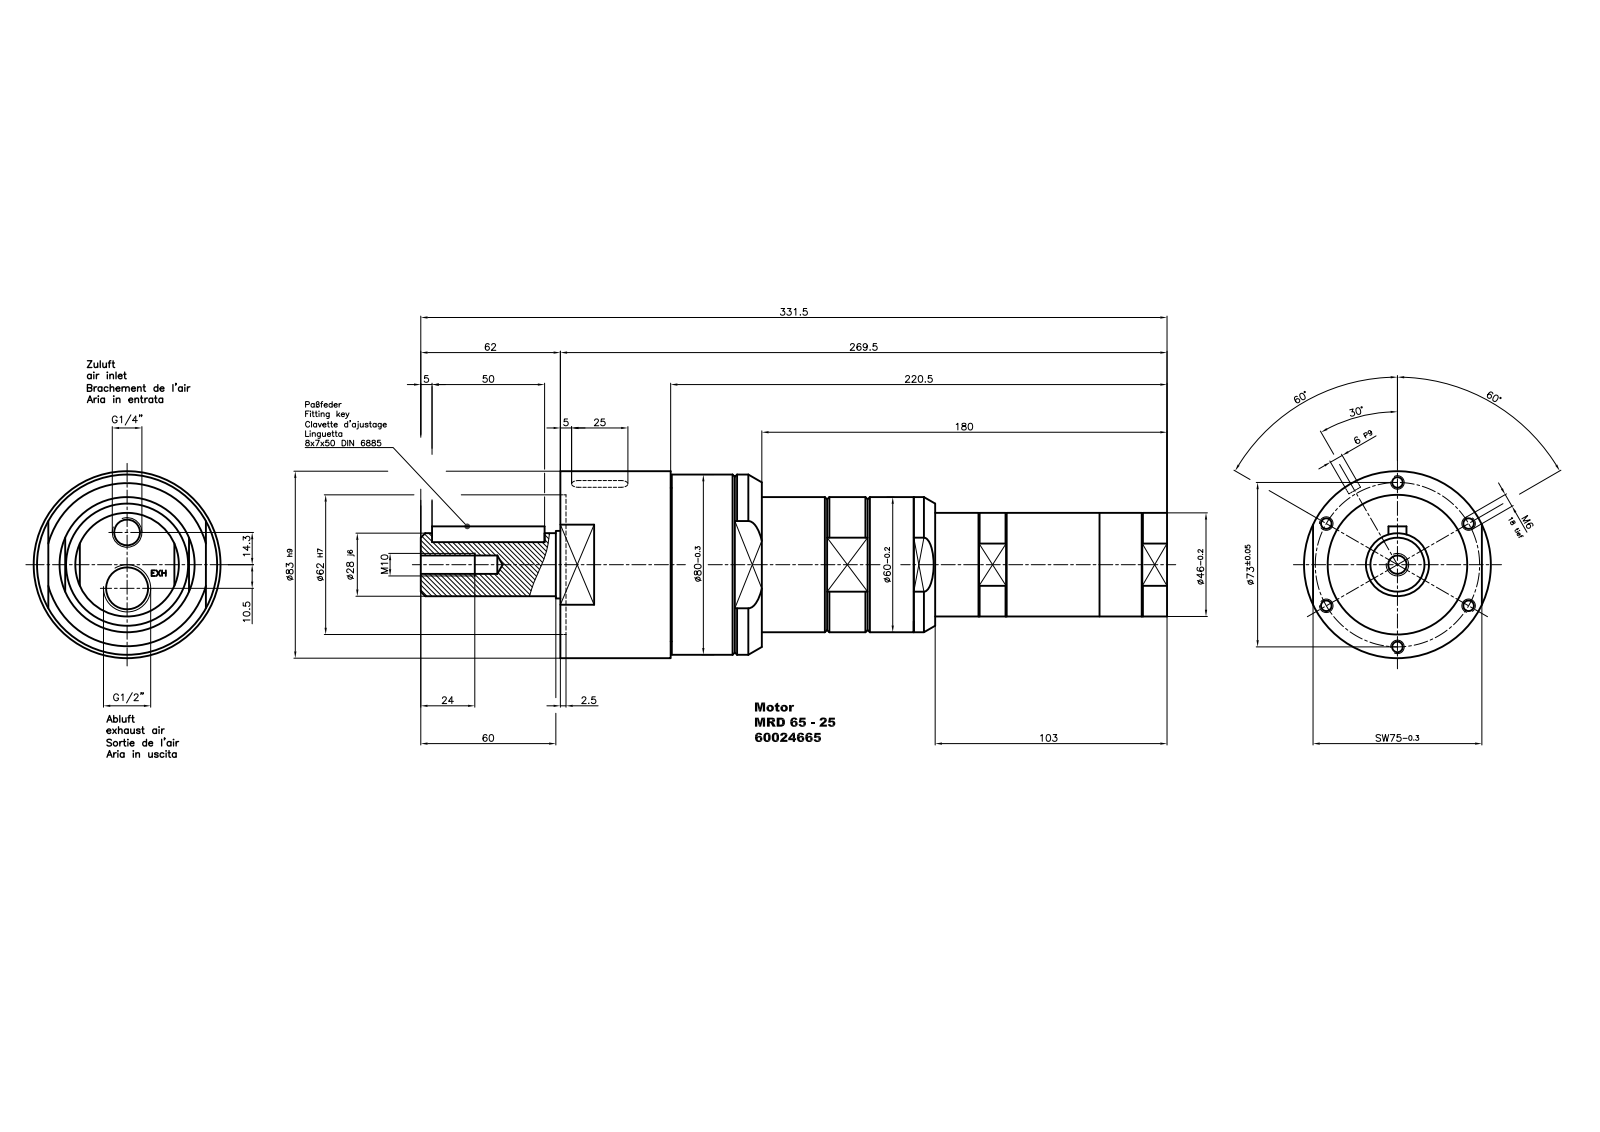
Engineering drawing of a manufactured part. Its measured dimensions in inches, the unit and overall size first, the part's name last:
Units: inches
Overall size (bounding box): 13.051 × 3.268 × 3.268
Round holes (diameter × count): ⌀0.194 ×5, ⌀0.061 ×2, ⌀0.098 ×2, ⌀0.217 ×2, ⌀0.194 ×1, ⌀0.33 ×1, ⌀0.451 ×1, ⌀0.733 ×1, ⌀1.496 ×1, ⌀1.831 ×1, ⌀2.311 ×1, ⌀2.441 ×1
Round bosses / shafts (diameter × count): ⌀0.197 ×2, ⌀3.268 ×1, ⌀3.15 ×1, ⌀2.683 ×1, ⌀2.362 ×1, ⌀1.811 ×1, ⌀1.772 ×1, ⌀1.181 ×1
Partial cylindrical surfaces — rounded edges, fillets, slot ends (radius × count): R0.089 ×2, R0.118 ×2, R0.157 ×2
Main face-to-face distances: 0.197, 1.929, 0.02, 1.732, 6.181, 5.984, 4.252, 1.831, 1.949, 1.752
Hole centre spacings: 1.437, 2.489, 2.874, 1.062, 1.12, 1.254, 1.281, 1.682
Volume: 52.71 in³ · Surface area: 131.9 in²
Bodies: 3 solids, 190 faces (100 planar, 52 cylindrical, 38 other)
Part name (STEP PRODUCT): MRD 65-331; 9314731 Sicherungsring
STEP written by: Autodesk Inventor 2012 (AUTOMOTIVE_DESIGN)
